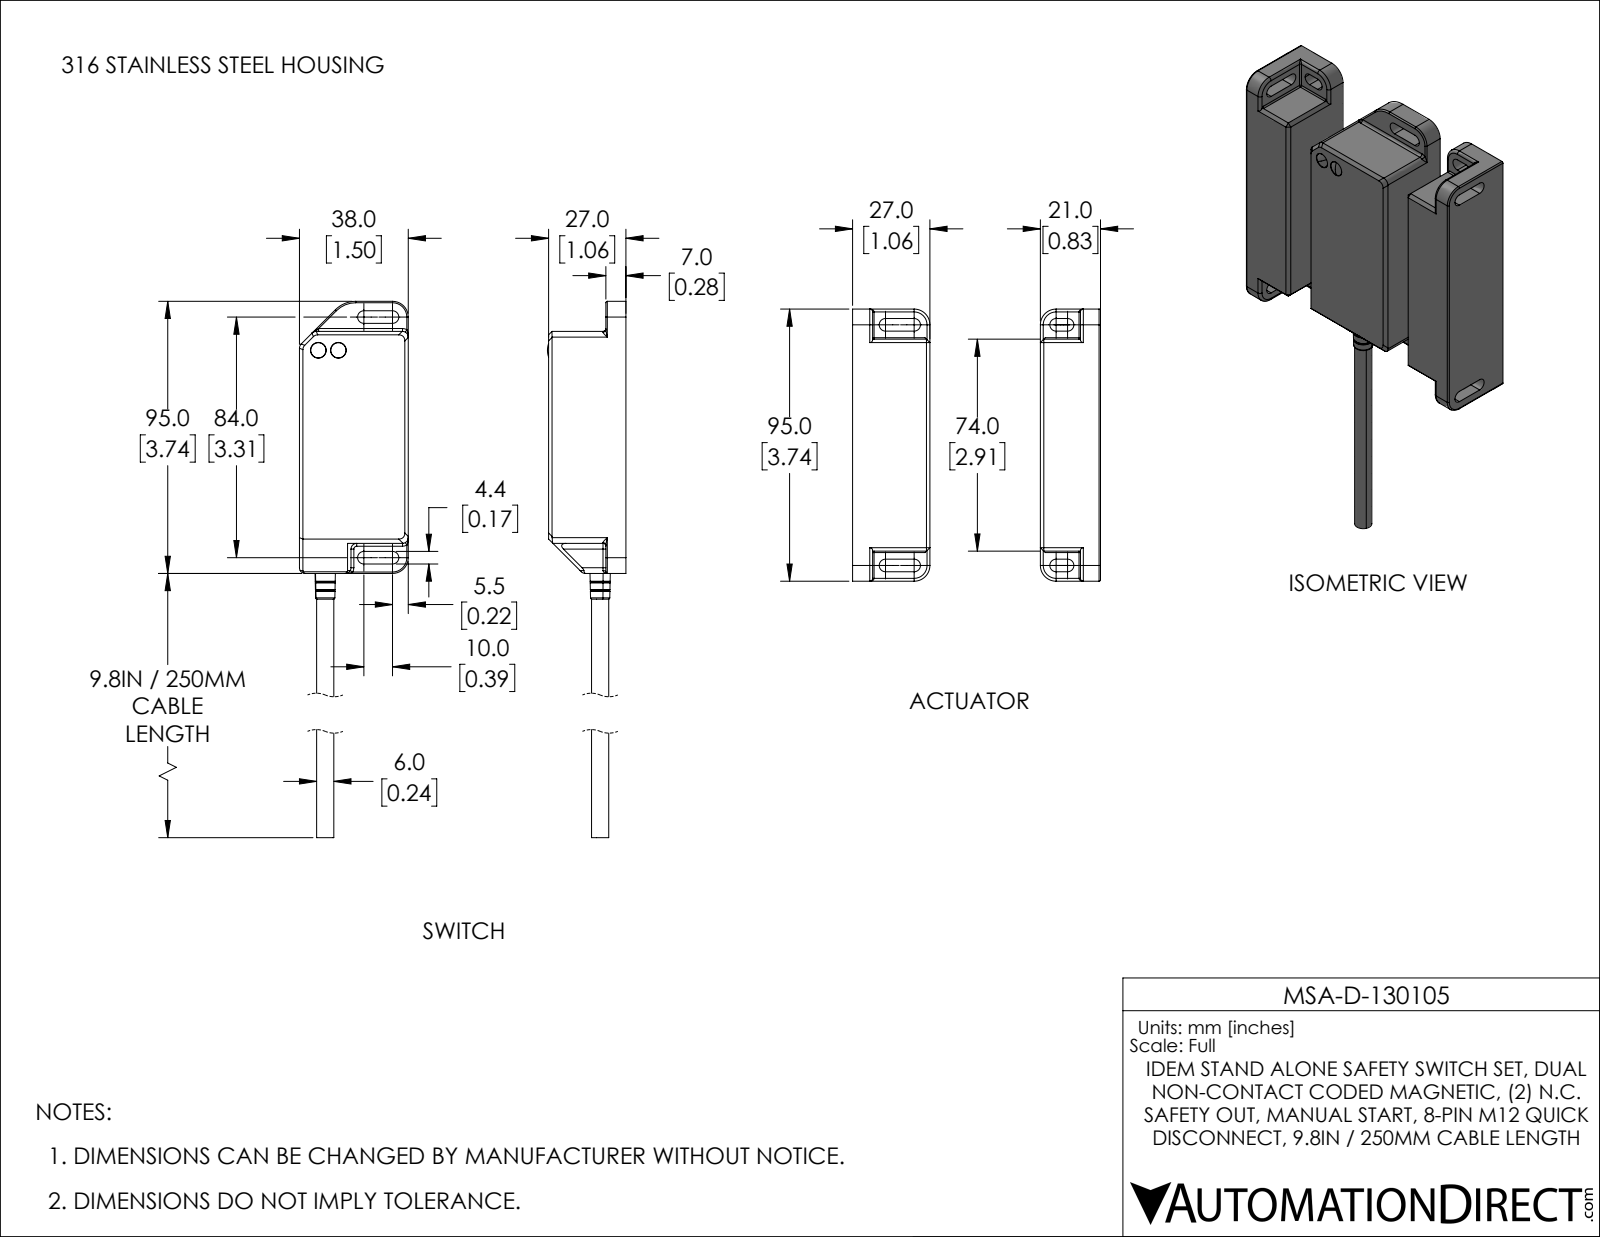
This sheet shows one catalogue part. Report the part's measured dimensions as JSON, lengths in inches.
{"part_name": "MSA-130102", "step_written_by": "SolidWorks 2019 (AUTOMOTIVE_DESIGN)", "units": "inches", "bodies": {"solids": 3, "faces": 1321, "planar": 640, "cylindrical": 332, "other": 349}, "overall_size": [7.092, 3.937, 1.079], "volume_in3": 4.099, "surface_area_in2": 94.51, "round_holes": [[0.116, 2], [0.217, 2], [0.323, 1]], "round_bosses_or_shafts": [[0.197, 3], [0.079, 3], [0.209, 2], [0.177, 2], [0.339, 1], [0.299, 1], [0.28, 1], [0.236, 1]], "partial_cylinders_radius": [[0.02, 113], [0.012, 16], [0.087, 16], [0.039, 15], [0.079, 10], [0.008, 8], [0.217, 8], [0.118, 4]], "face_to_face_distances": [0.079, 1.89, 3.11, 1.22, 0.472, 0.748, 2.638, 2.717, 1.055, 0.976], "hole_center_spacings": [0.276]}
